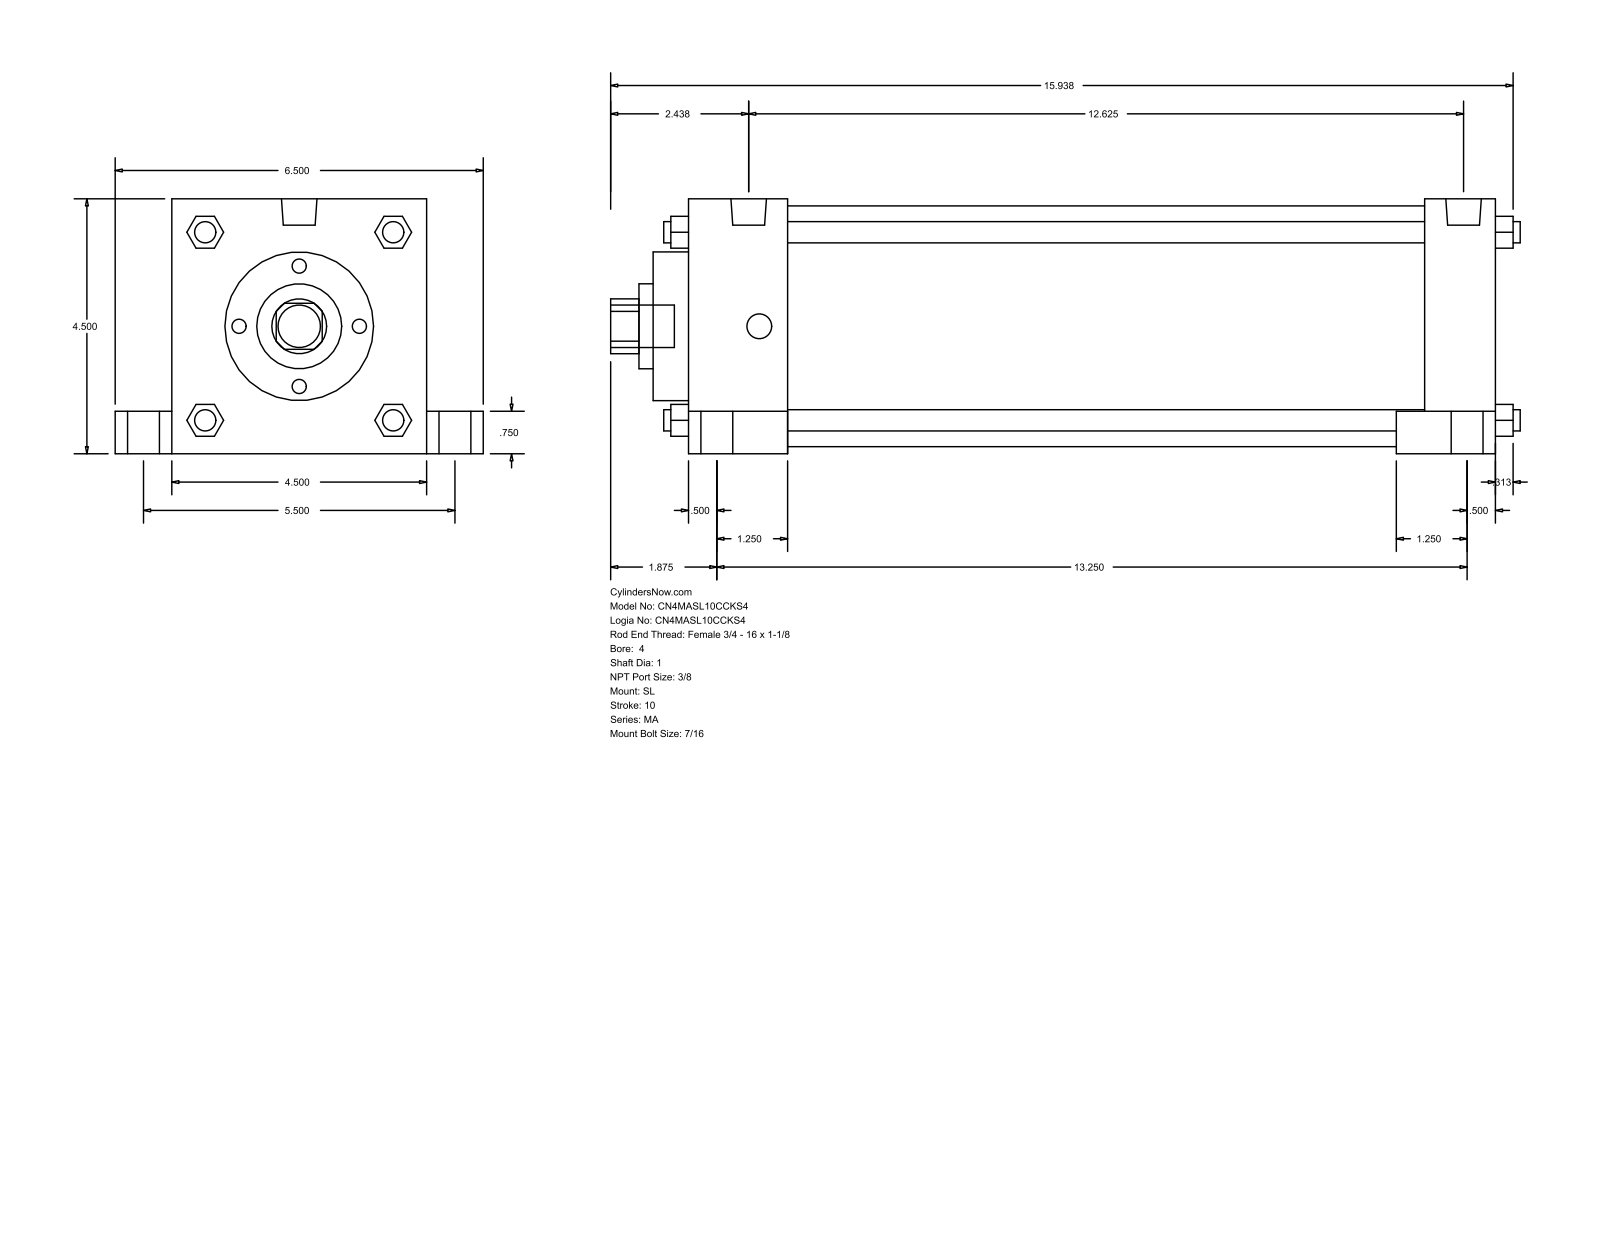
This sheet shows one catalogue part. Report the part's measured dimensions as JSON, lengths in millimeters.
{"part_name": "MA_SL__0400_1", "step_written_by": "GSSL Pune (CONFIG_CONTROL_DESIGN)", "units": "millimeters", "bodies": {"solids": 0, "faces": 150, "planar": 113, "cylindrical": 37, "other": 0}, "overall_size": [407.99, 165.1, 114.3], "round_holes": [[25.4, 1], [38.1, 1], [66.67, 1], [107.95, 1]], "round_bosses_or_shafts": [[20.64, 4], [14.29, 4], [11.11, 4], [9.53, 4], [15.93, 2], [19.05, 1]], "partial_cylinders_radius": [[12.29, 1]], "face_to_face_distances": [114.3, 361.96, 44.46, 317.5, 330.2, 285.74, 31.76, 25.4, 139.7, 19.05]}
